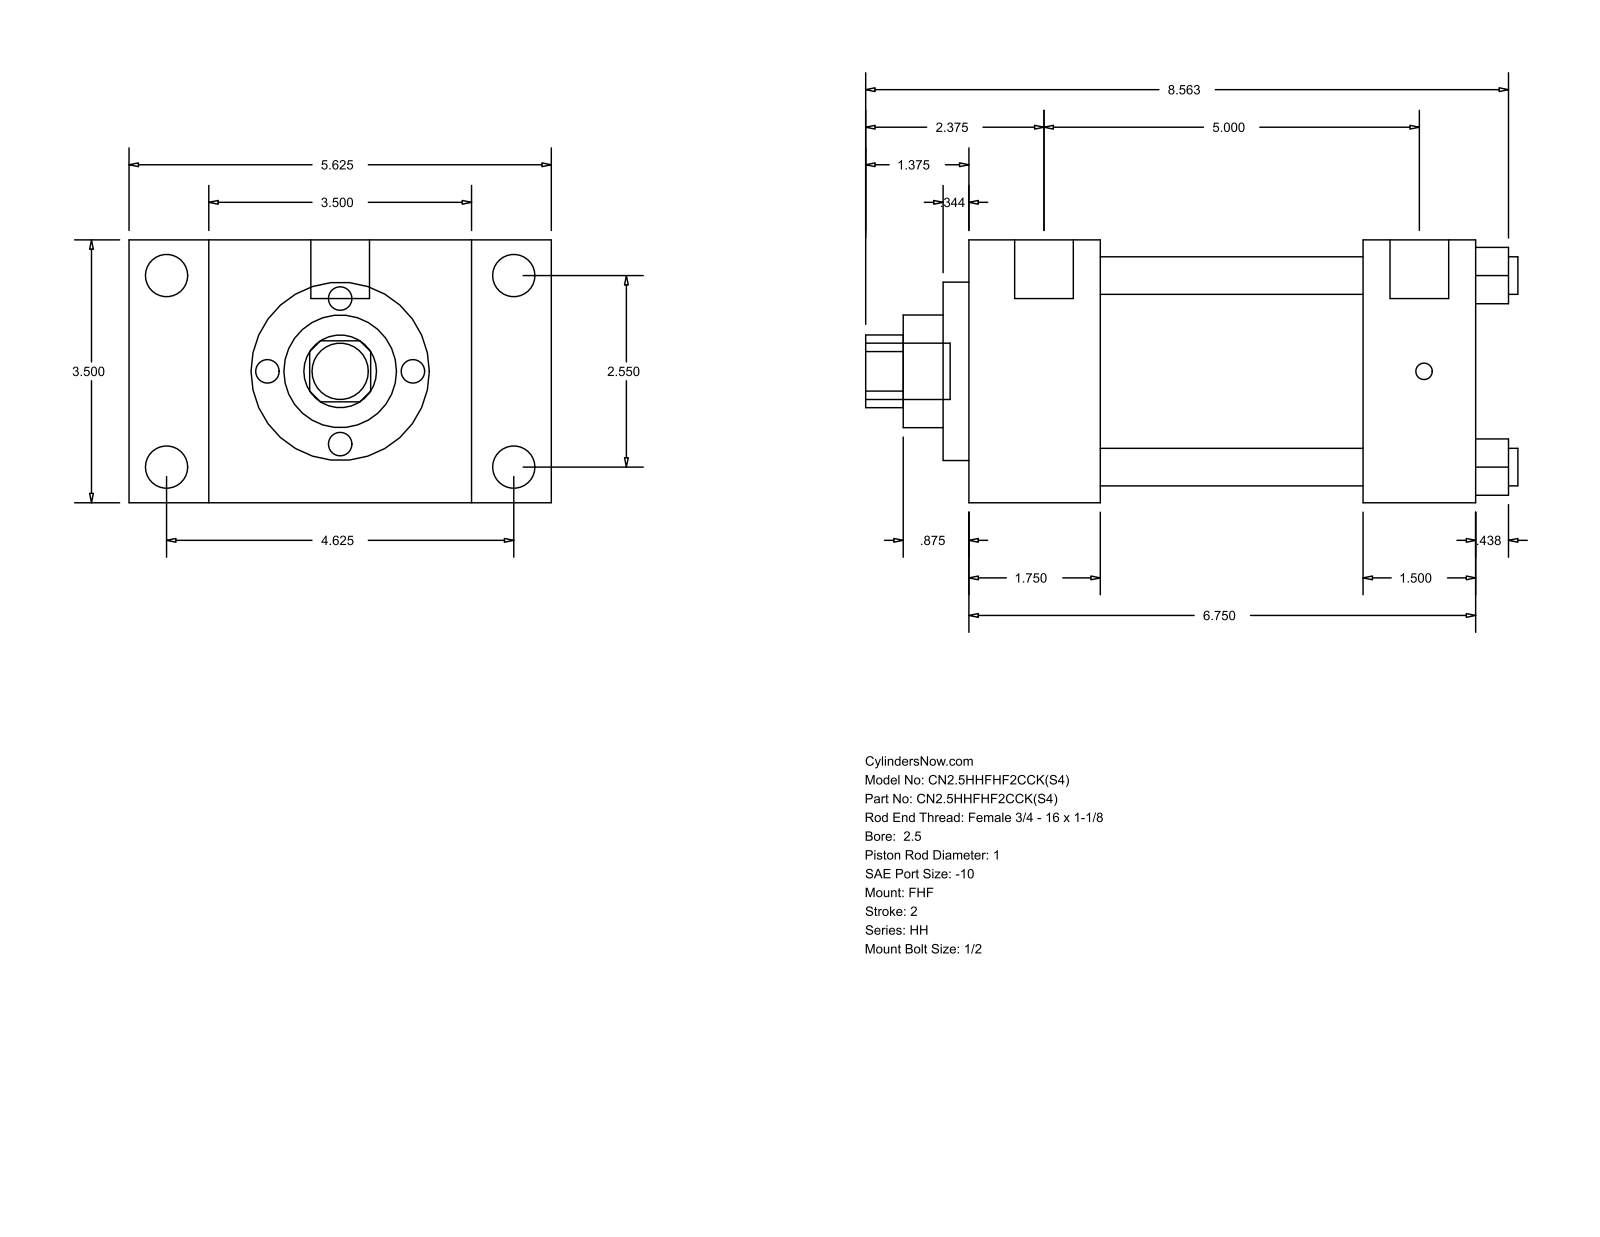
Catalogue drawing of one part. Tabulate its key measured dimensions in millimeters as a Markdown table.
| quantity | value |
| --- | --- |
| part name | HH_FHF__0250_1 |
| STEP written by | GSSL Pune (CONFIG_CONTROL_DESIGN) |
| units | millimeters |
| bodies | 0 solids, 90 faces (61 planar, 29 cylindrical, 0 other) |
| overall size | 220.66 × 142.88 × 88.9 |
| round holes (diameter × count) | 12.7 × 4, 25.4 × 1, 38.1 × 1, 60.33 × 1, 73.03 × 1 |
| round bosses / shafts (diameter × count) | 14.3 × 4, 5.56 × 4, 19.84 × 2, 19.05 × 1 |
| partial cylindrical surfaces (radius × count) | 12.29 × 1 |
| main face-to-face distances | 88.9, 44.46, 26.99, 115.89, 171.46, 127, 142.88, 133.36, 38.1, 8.73 |
| hole center spacings | 45.79, 64.76, 91.58 |
